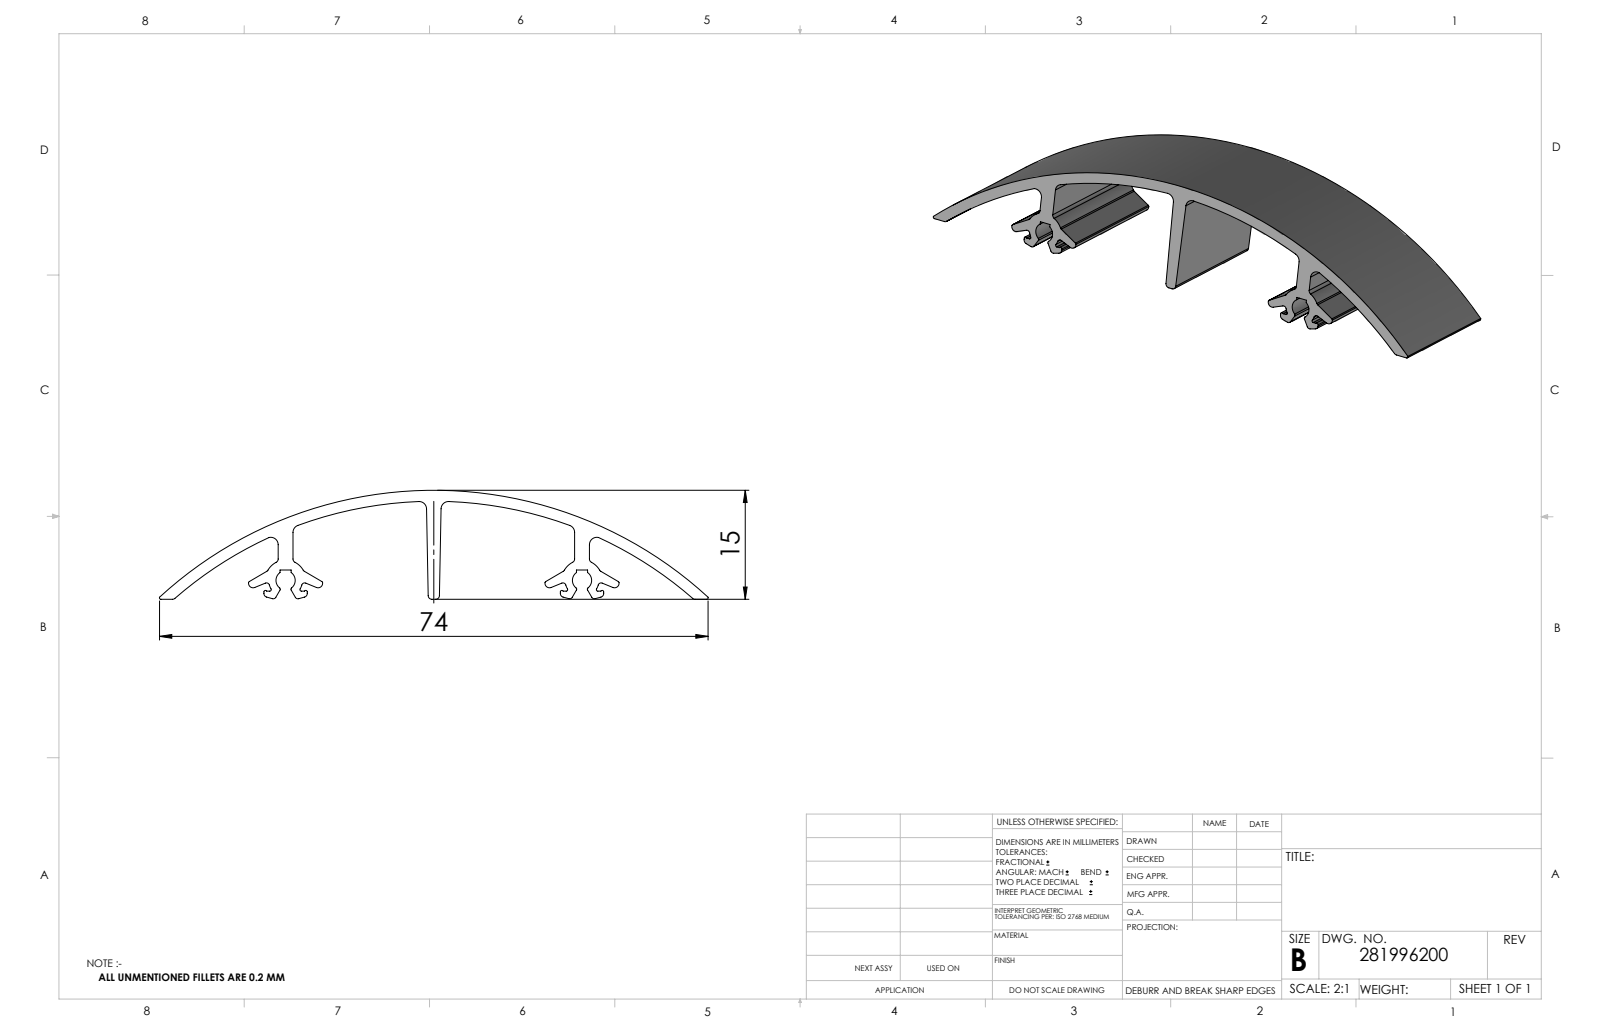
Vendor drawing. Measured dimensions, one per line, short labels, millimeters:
name: 281996200_c_1
written by: SolidWorks 2014 (CONFIG_CONTROL_DESIGN)
unit: mm
bodies: 1 solid, 118 faces (41 planar, 77 cylindrical, 0 other)
size: 74.05 × 20 × 14.7
volume: 4 036 mm³; area: 5 740 mm²
rounds: 18× R0.2, 12× R0.4, 12× R0.5, 6× R1, 4× R0.61, 2× R1.3, 2× R2.27, 2× R2.75
face distances: 20, 20.2, 40, 2, 38, 15.16, 3.95, 34.64, 42, 1.1
